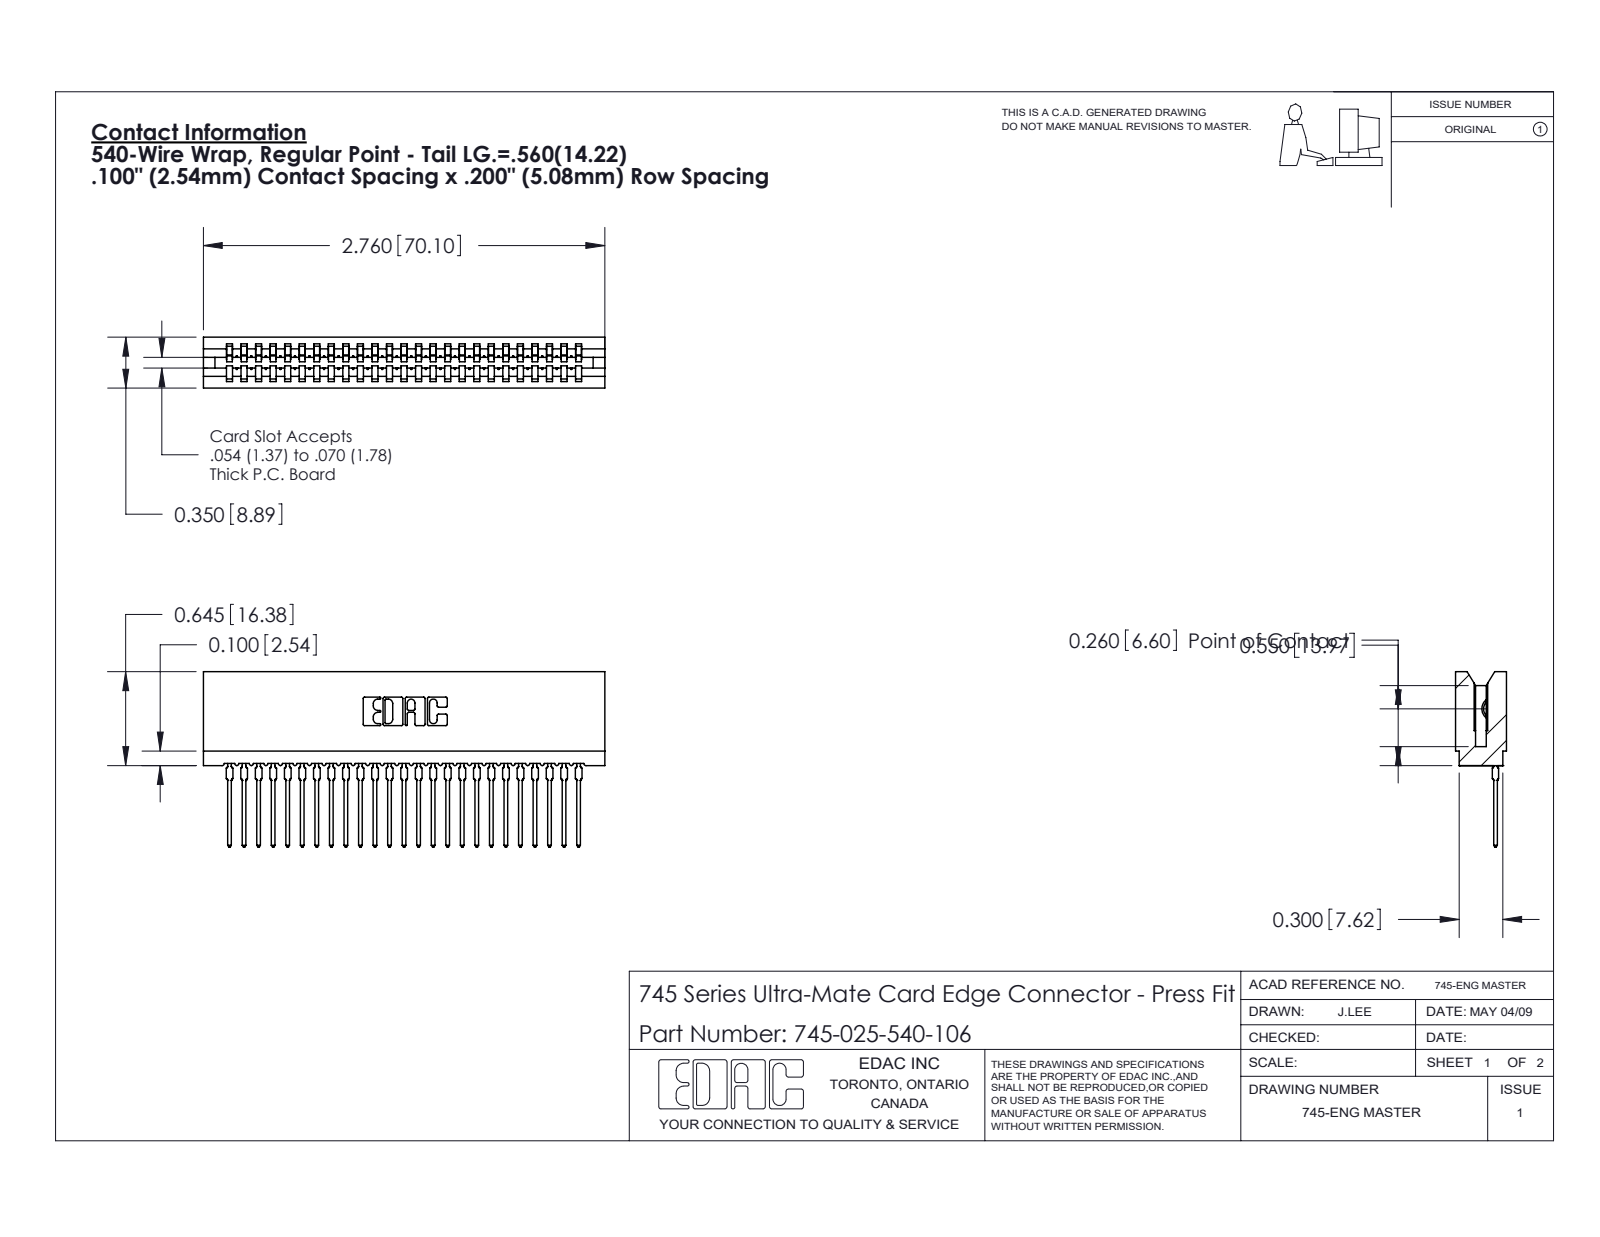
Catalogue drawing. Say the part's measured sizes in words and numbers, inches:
The part is named "745-292-001_540; 745-025-540-106; 745 Part_Insulator Option - 06". Its 3-D file was written by "SolidWorks 2020 (CONFIG_CONTROL_DESIGN)". It is 26 solids with 2896 faces: 1731 planar, 515 cylindrical and 650 other. Overall it measures 2.76 by 1.206 by 0.35 inches. Its volume is 0.38 cubic inches and its surface area 17.91 square inches. Partial cylindrical surfaces (rounded edges, fillets, slot ends): 50 of radius 0.015, 50 of radius 0.021, 22 of radius 0.01, 6 of radius 0.007, 6 of radius 0.031, 4 of radius 0.005, 4 of radius 0.011, 3 of radius 0.026. The main face-to-face distances are 0.1, 0.2, 0.35, 0.3, 0.4, 0.5, 0.138, 0.212, 0.045, 0.305.
